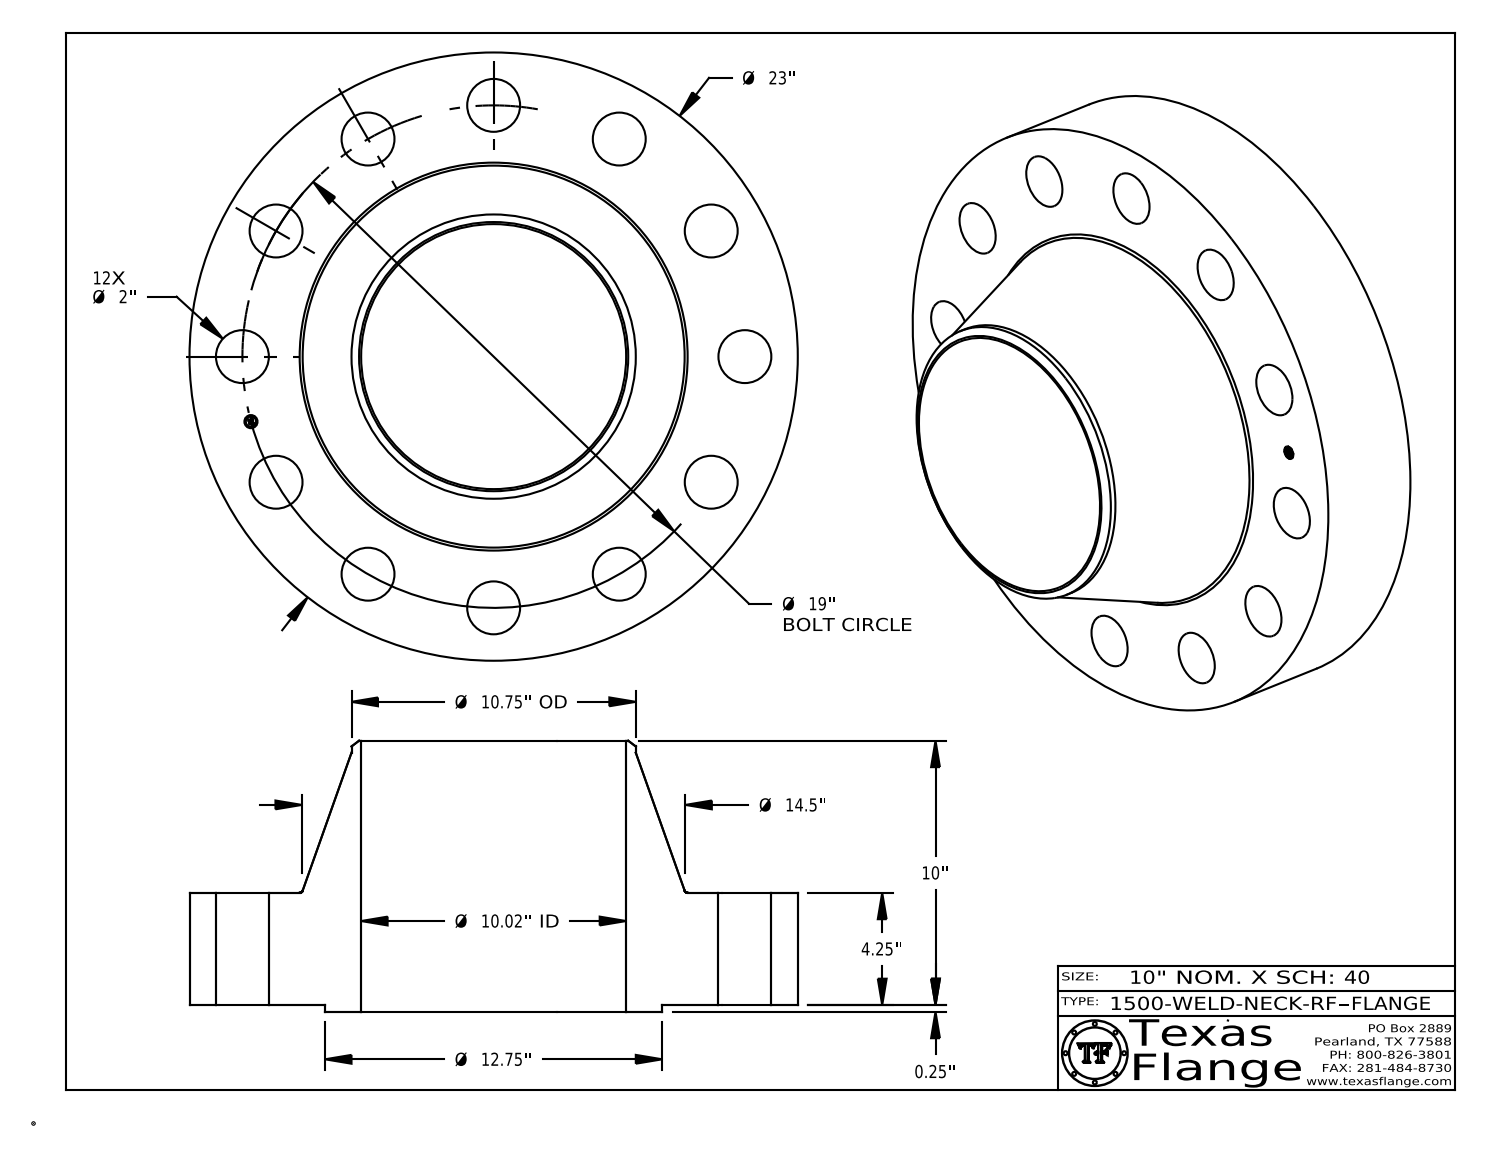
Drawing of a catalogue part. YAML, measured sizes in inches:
part_name: "1500-WELD-NECK-RF"
step_written_by: "CATIA V5 STEP AP214 (AUTOMOTIVE_DESIGN)"
units: inches
bodies: {solids: 1, faces: 427, planar: 369, cylindrical: 52, other: 6}
overall_size: [23, 23, 10.25]
volume: 1537
surface_area: 1716
round_holes:
  - {diameter: 2, count: 12}
  - {diameter: 0.495, count: 1}
  - {diameter: 10.02, count: 1}
round_bosses_or_shafts:
  - {diameter: 0.03, count: 8}
  - {diameter: 23, count: 1}
  - {diameter: 12.75, count: 1}
  - {diameter: 10.75, count: 1}
  - {diameter: 0.39, count: 1}
face_to_face_distances: [4.25, 0.25, 4.5, 10.25, 10, 5.75, 4.485, 4.235, 0.015, 5.765]
hole_center_spacings: [9.5, 13.435, 16.454, 18.352, 4.918, 19, 4.917, 15.074]
